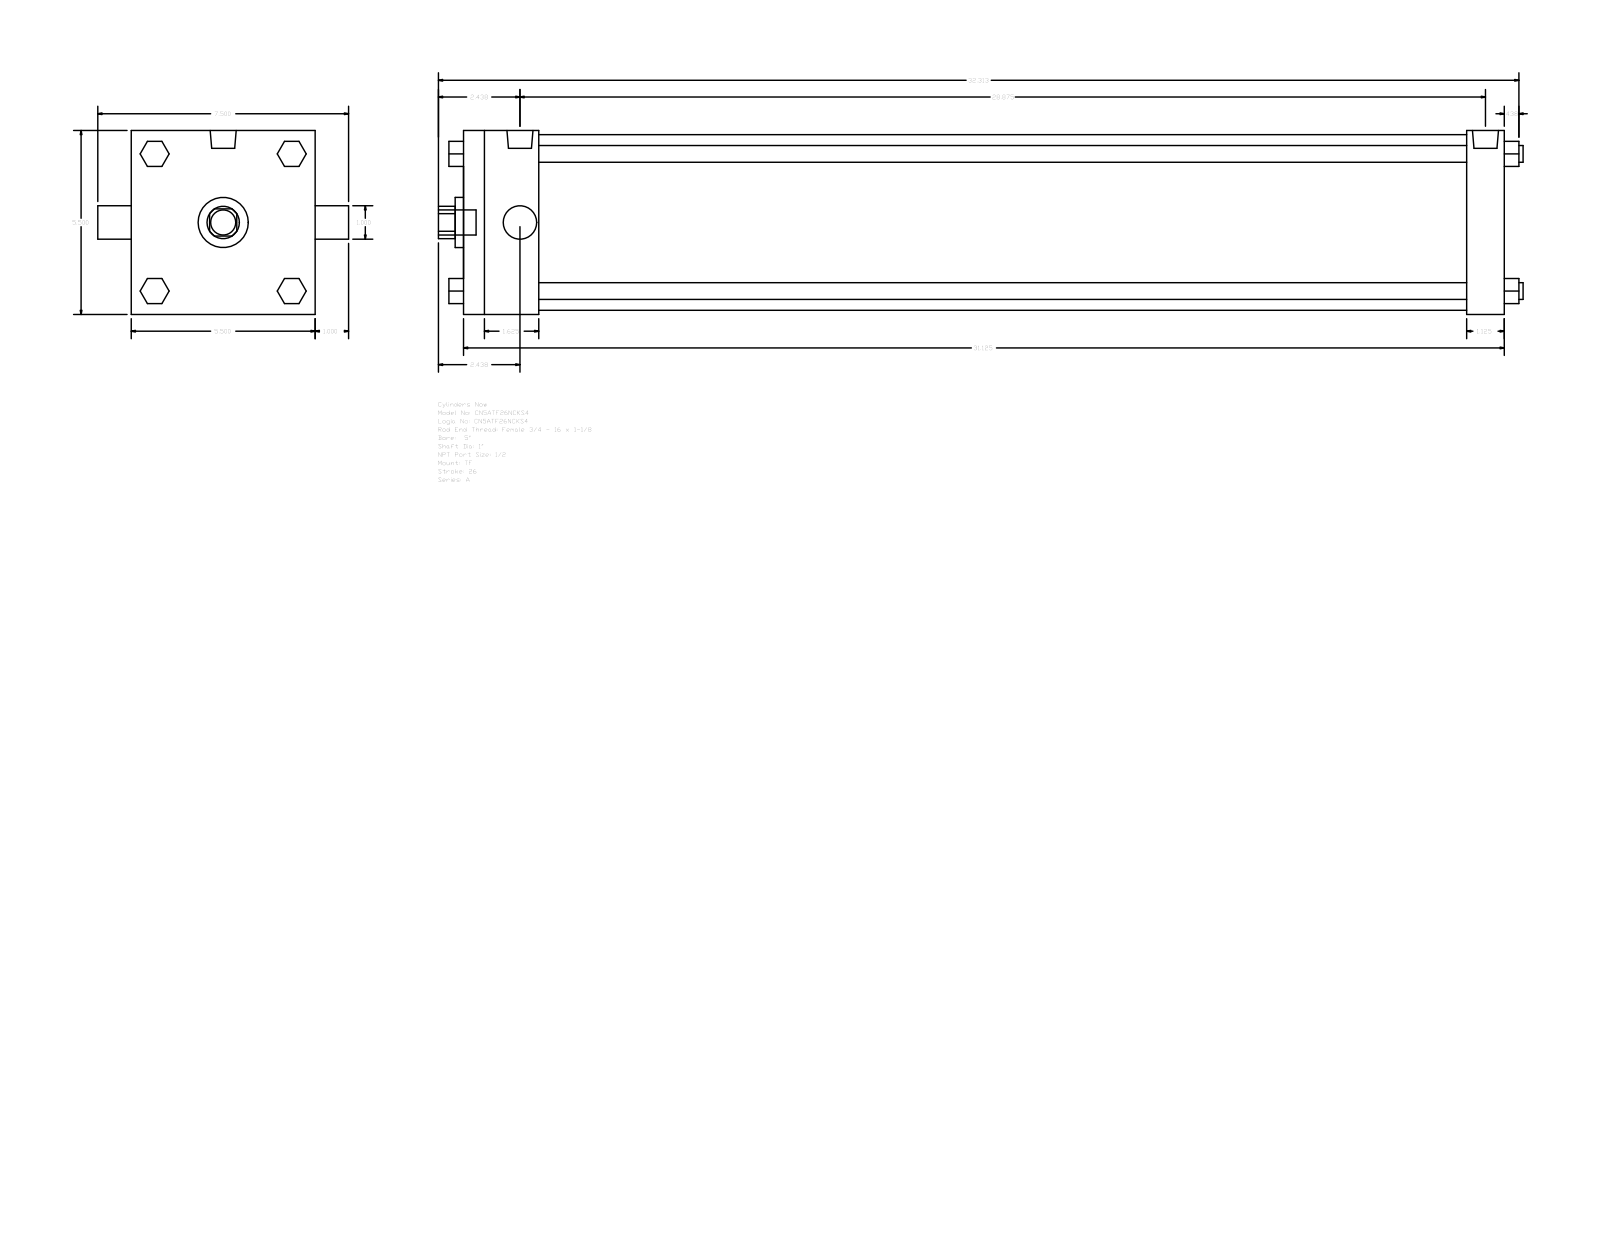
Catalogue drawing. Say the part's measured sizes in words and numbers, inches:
The part is named "A_TF__0500_1". Its 3-D file was written by "GSSL Pune (CONFIG_CONTROL_DESIGN)". It is 0 solids with 120 faces: 92 planar, 28 cylindrical and 0 other. Overall it measures 32.437 by 7.5 by 5.5 inches. Round holes: 2 of diameter 1, 1 of diameter 1.5, 1 of diameter 5.25. Round bosses or shafts: 4 of diameter 0.5, 3 of diameter 0.344, 2 of diameter 0.778, 1 of diameter 0.75. Partial cylindrical surfaces (rounded edges, fillets, slot ends): 1 of radius 0.484. The main face-to-face distances are 5.5, 31.125, 1.125, 30, 2.25, 27.75, 28.875, 0.75, 2.05, 3.55.
